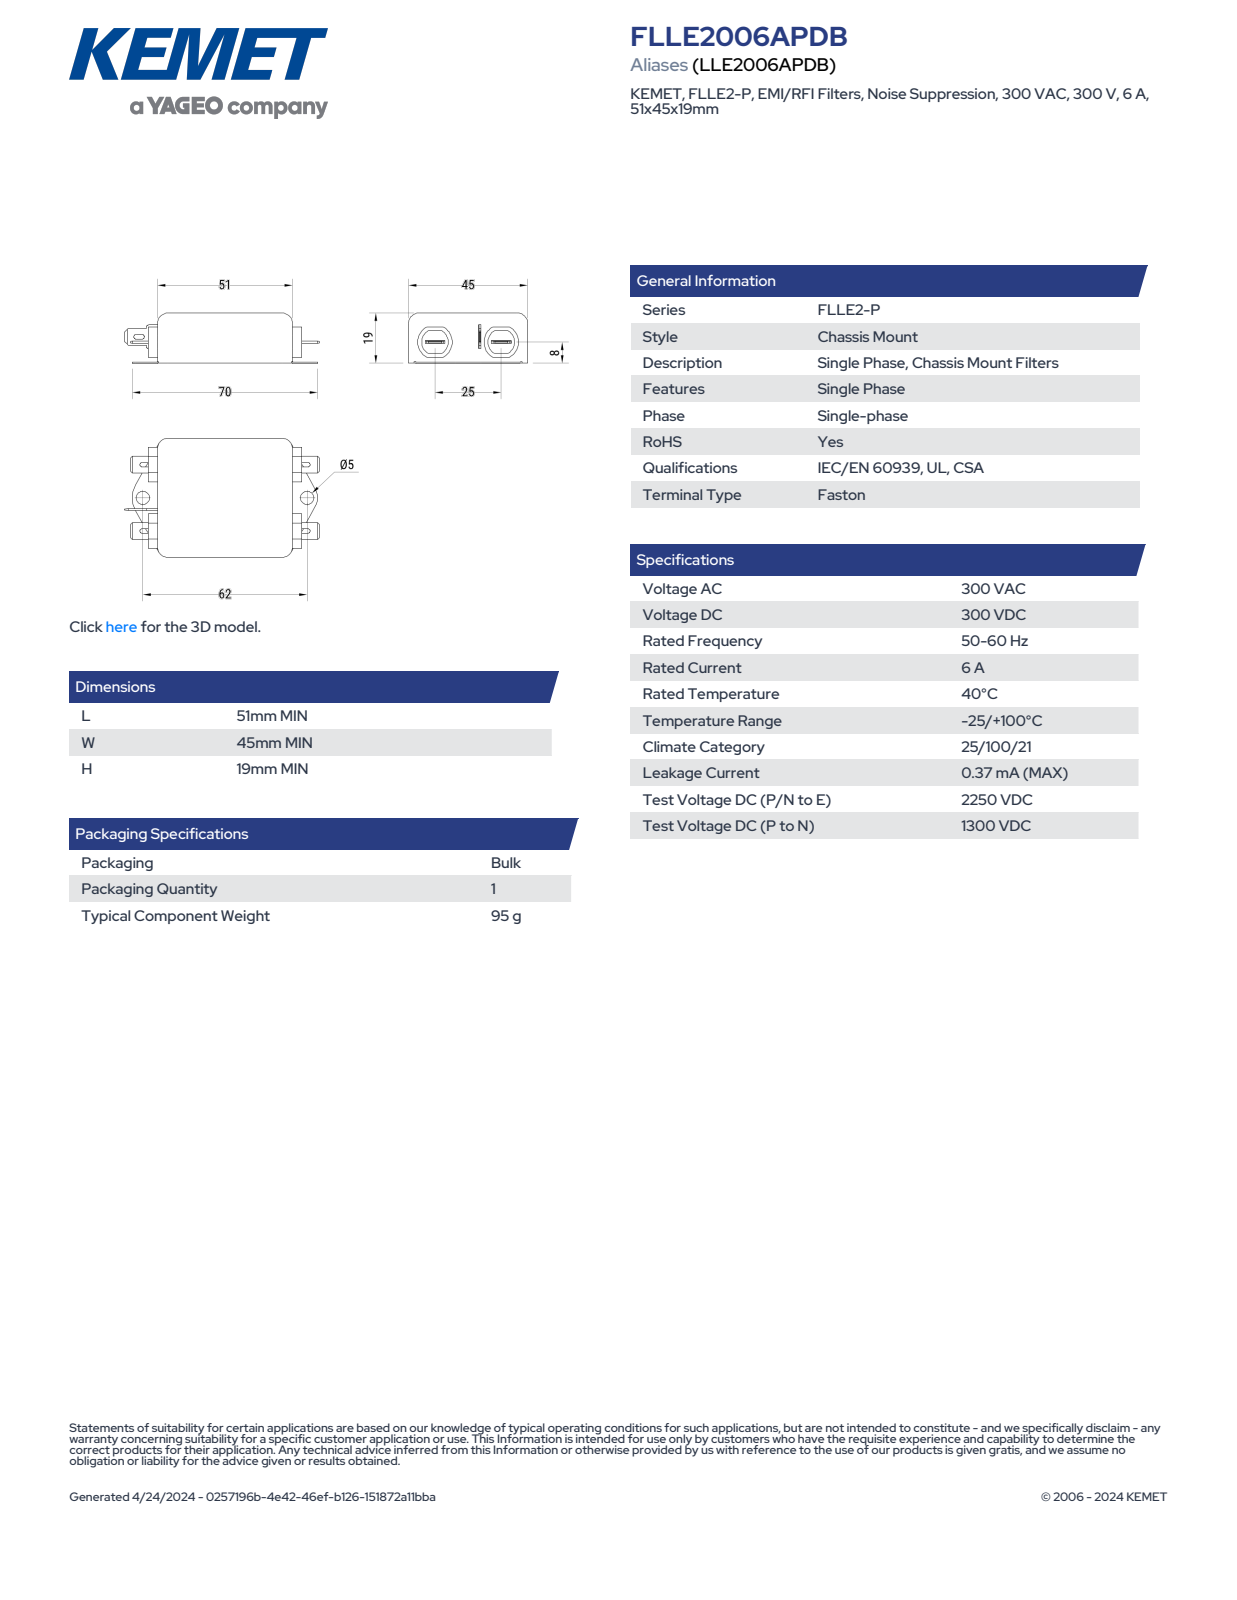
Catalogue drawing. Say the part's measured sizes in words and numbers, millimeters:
The part is named "GEH0681asm; Case; Earth; Fast-on (+3 more)". Its 3-D file was written by "Spatial InterOp 3D (automotive_design)". It is 11 solids with 427 faces: 312 planar, 95 cylindrical and 20 other. Overall it measures 73.56 by 45 by 19 millimeters. Its volume is 43 338 cubic millimeters and its surface area 21 772 square millimeters. Round holes: 4 of diameter 2.4, 2 of diameter 5. Partial cylindrical surfaces (rounded edges, fillets, slot ends): 10 of radius 0.9, 8 of radius 3.5, 8 of radius 4, 4 of radius 0.6, 4 of radius 0.7, 4 of radius 1.2, 4 of radius 1.75, 2 of radius 0.2. The main face-to-face distances are 0.5, 17.8, 18.3, 44.5, 44, 50.5, 50, 18.5, 45, 51. The hole center spacings are 16.65, 52.51, 25, 40, 47.17, 62.
